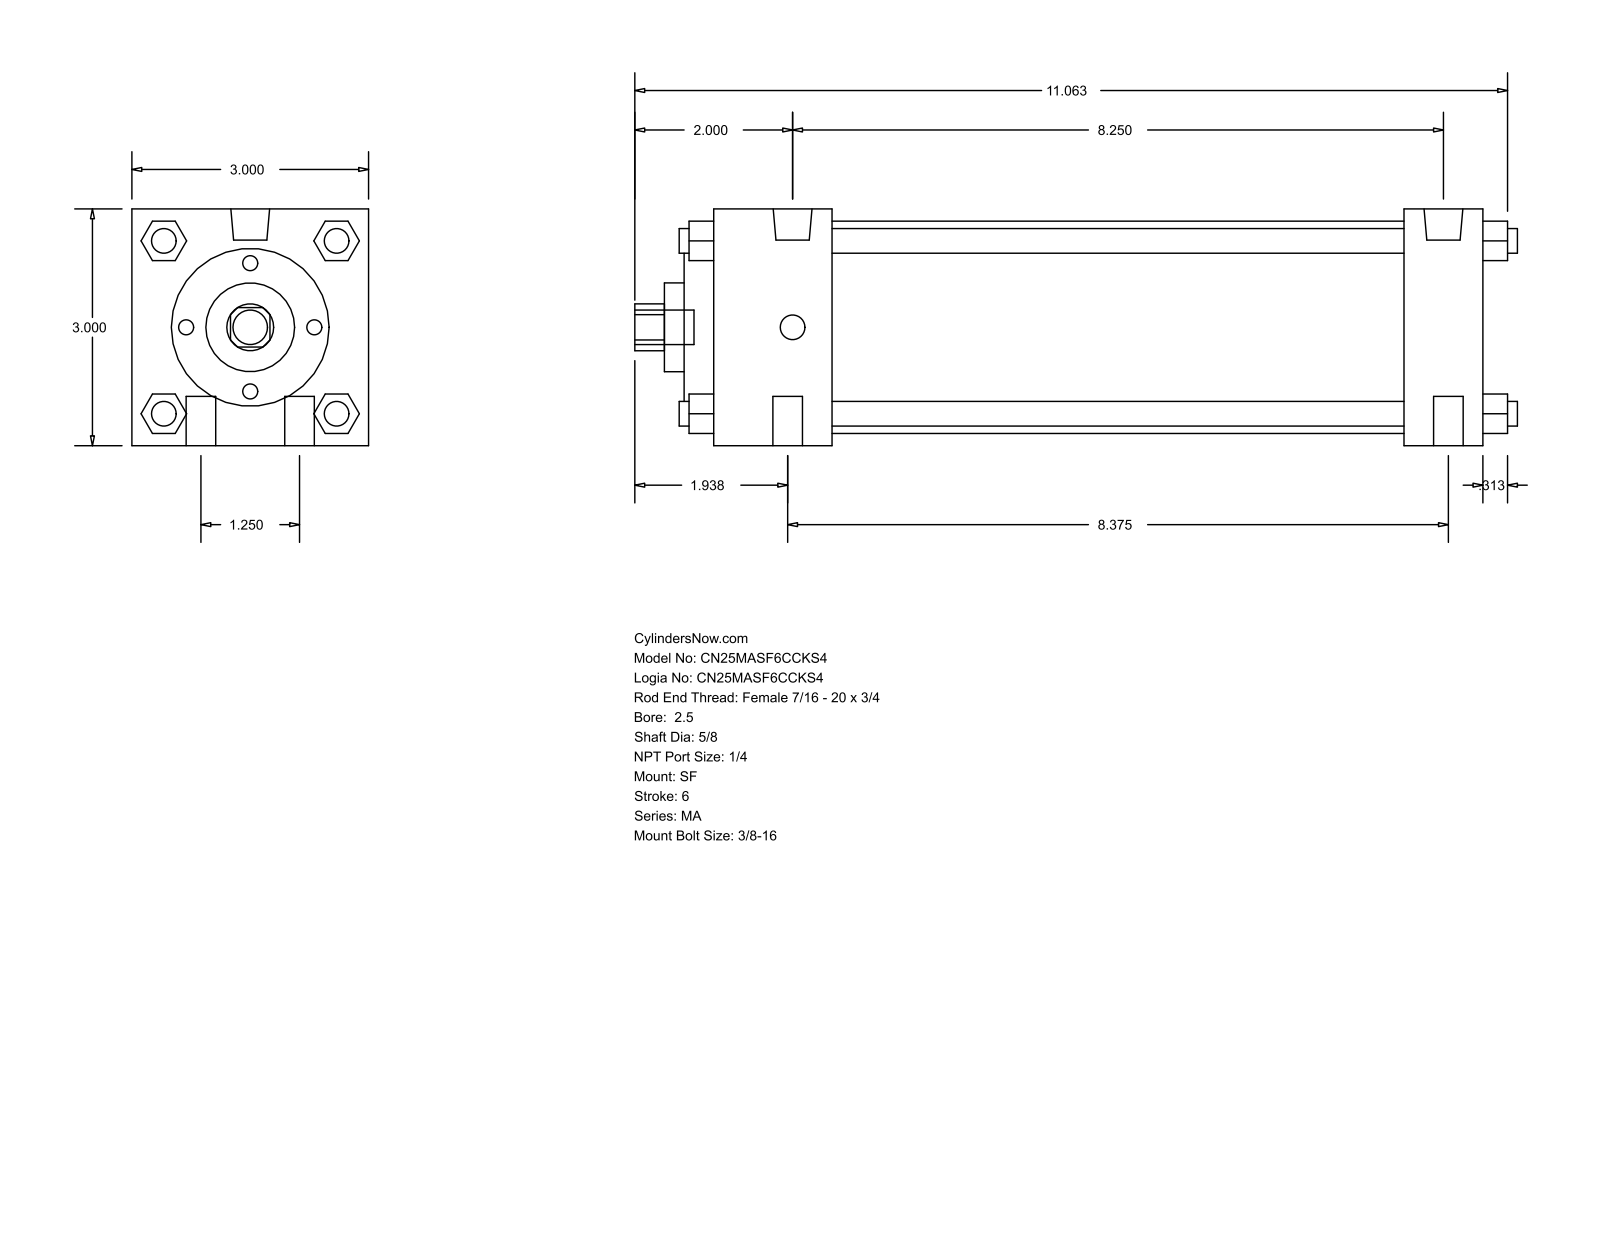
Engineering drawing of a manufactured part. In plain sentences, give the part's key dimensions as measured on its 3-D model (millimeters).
The part is named "MA_SF__0250_0.625". Its 3-D file was written by "GSSL Pune (CONFIG_CONTROL_DESIGN)". It is 0 solids with 126 faces: 95 planar, 31 cylindrical and 0 other. Overall it measures 284.16 by 76.2 by 76.2 millimeters. Round holes: 1 of diameter 15.88, 1 of diameter 28.57, 1 of diameter 50.8, 1 of diameter 68.33. Round bosses or shafts: 6 of diameter 7.94, 4 of diameter 9.53, 2 of diameter 12.49, 1 of diameter 11.11. Partial cylindrical surfaces (rounded edges, fillets, slot ends): 1 of radius 7.54. The main face-to-face distances are 76.2, 247.65, 25.4, 222.25, 38.1, 184.15, 209.55, 12.7, 9.52, 47.62.
